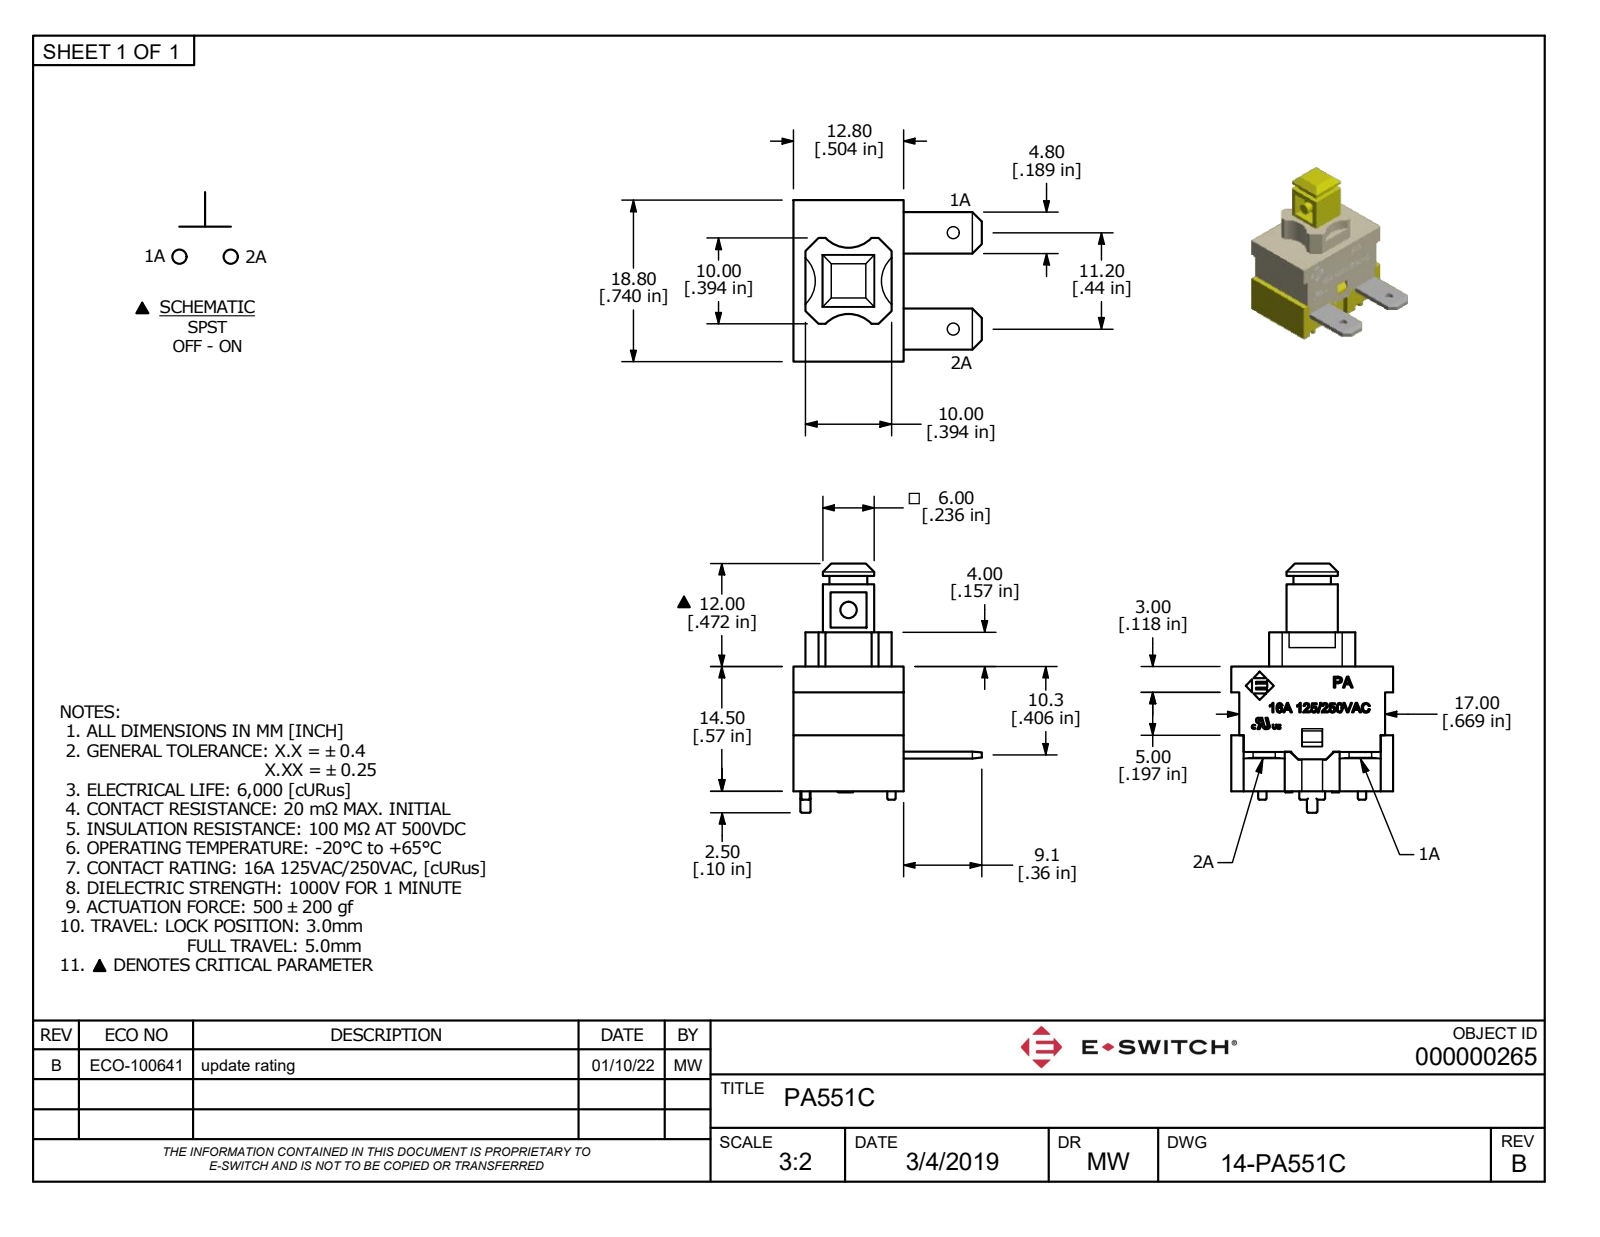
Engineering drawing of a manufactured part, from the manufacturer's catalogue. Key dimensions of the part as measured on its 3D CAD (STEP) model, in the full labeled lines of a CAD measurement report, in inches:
Part name (STEP PRODUCT): PA551C
STEP written by: Autodesk Inventor 2022 (AUTOMOTIVE_DESIGN)
Units: inches
Bodies: 1 solid, 752 faces (558 planar, 64 cylindrical, 130 other)
Overall size (bounding box): 1.142 × 0.862 × 0.74
Volume: 0.13 in³ · Surface area: 6.722 in²
Round holes (diameter × count): ⌀0.055 ×2, ⌀0.118 ×1
Round bosses / shafts (diameter × count): ⌀0.037 ×4, ⌀0.098 ×1, ⌀0.075 ×1
Partial cylindrical surfaces — rounded edges, fillets, slot ends (radius × count): R0.01 ×17, R0.005 ×16, R0.006 ×8, R0.146 ×4, R0.02 ×1, R0.039 ×1, R0.07 ×1, R0.091 ×1
Main face-to-face distances: 0.031, 0.472, 0.035, 0.661, 0.079, 0.441, 0.339, 0.173, 0.435, 0.043
Hole centre spacings: 0.528, 0.441
